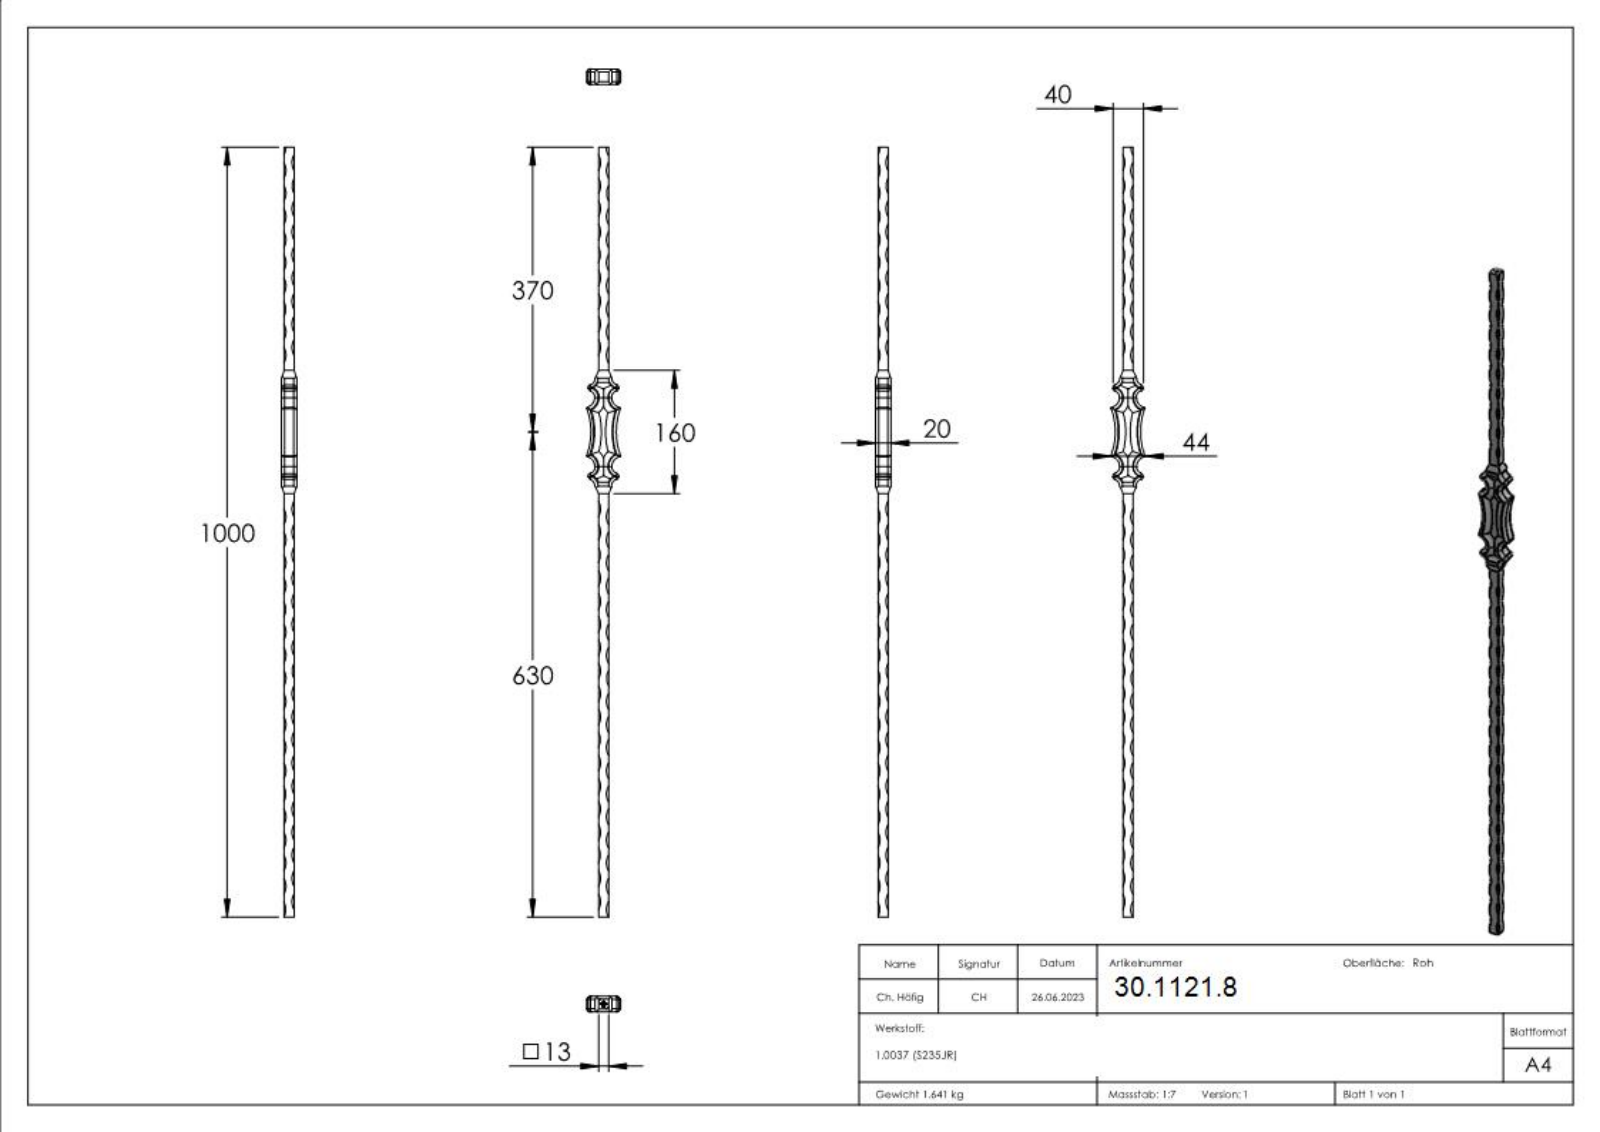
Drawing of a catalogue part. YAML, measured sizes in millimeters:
part_name: "1249"
step_written_by: "SolidWorks 2018 (CONFIG_CONTROL_DESIGN)"
units: millimeters
bodies: {solids: 1, faces: 463, planar: 152, cylindrical: 46, other: 265}
overall_size: [1000, 44, 20]
volume: 210431
surface_area: 59936
partial_cylinders:
  - {radius: 4, count: 12}
  - {radius: 9, count: 8}
  - {radius: 1.5, count: 4}
  - {radius: 10, count: 4}
  - {radius: 13, count: 4}
  - {radius: 14, count: 4}
  - {radius: 88.21, count: 2}
face_to_face_distances: [13, 1.5, 11.5, 5, 3.5, 15, 16.5, 10, 20, 65.22]
